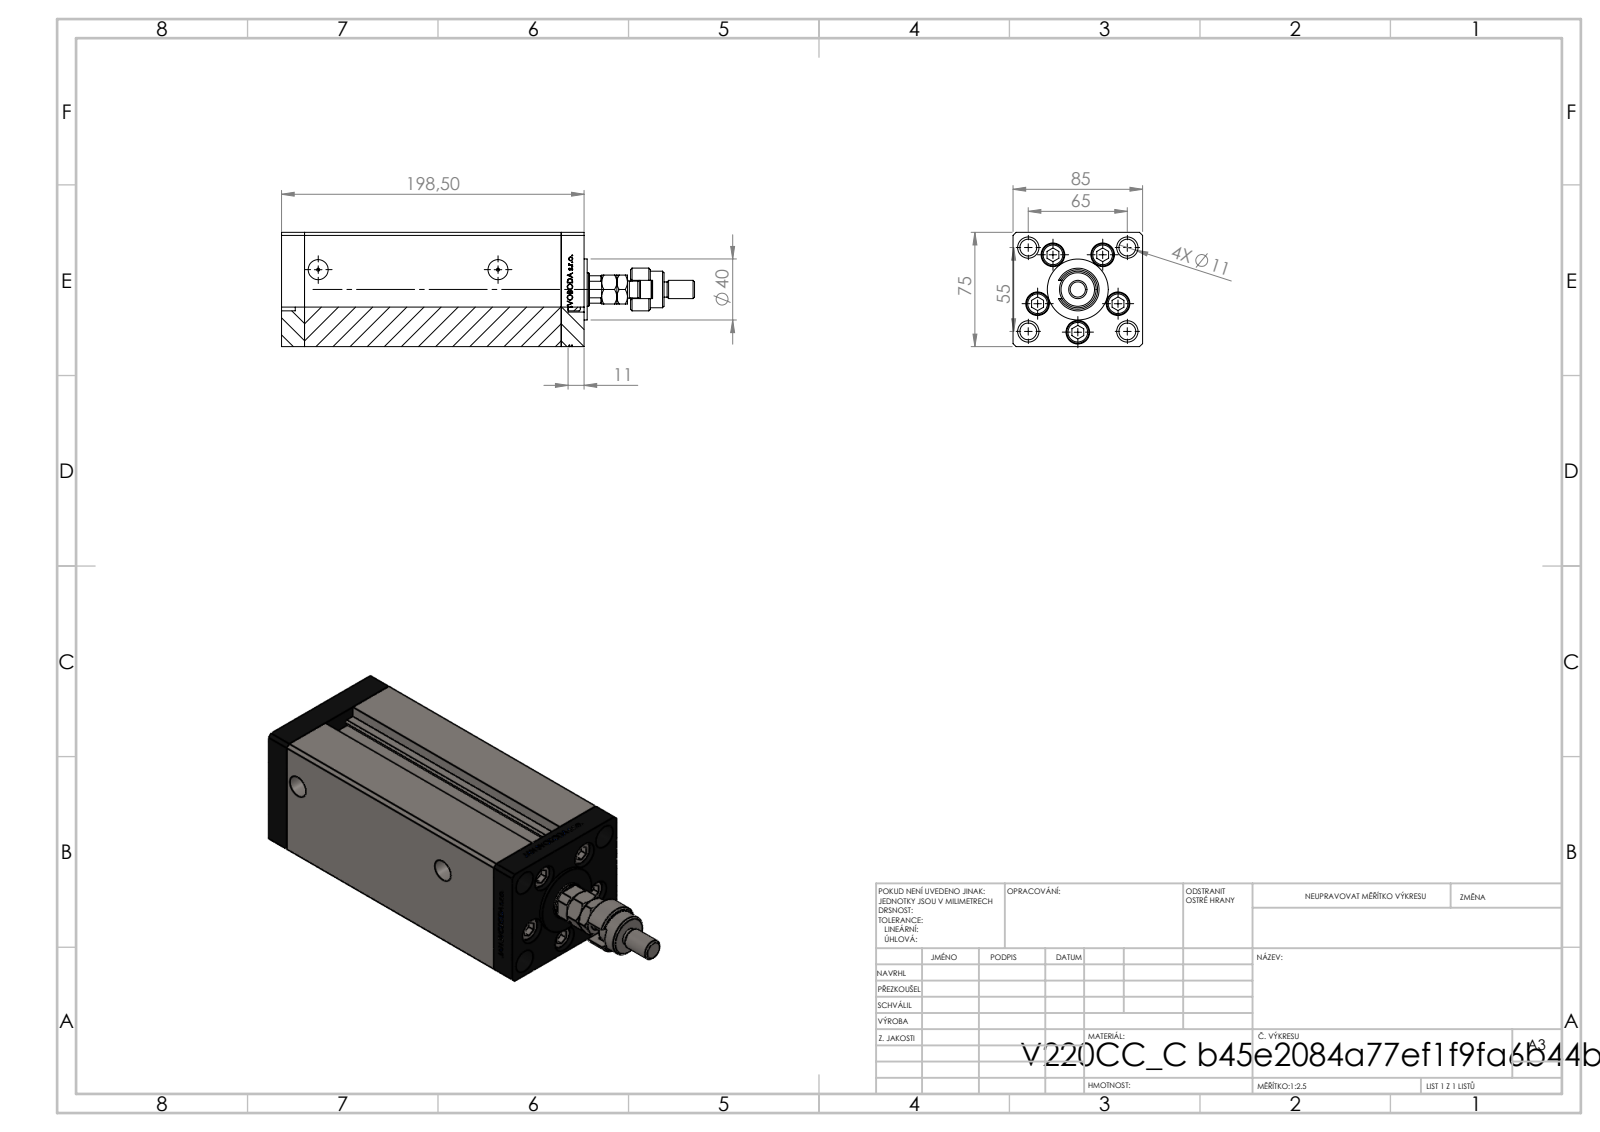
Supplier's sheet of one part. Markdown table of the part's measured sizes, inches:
| quantity | value |
| --- | --- |
| part name | V220C BACK_C; ALLEN BOLT; MFA; FEMALE_PART_FOR_DFA (+3 more) |
| STEP written by | SolidWorks 2019 (CONFIG_CONTROL_DESIGN) |
| units | inches |
| bodies | 15 solids, 1260 faces (574 planar, 180 cylindrical, 506 other) |
| overall size | 10.669 × 3.346 × 2.953 |
| volume | 64.87 in³ |
| surface area | 311.9 in² |
| round holes (diameter × count) | 0.433 × 9, 0.61 × 5, 0.394 × 4, 0.551 × 4, 0.079 × 2, 0.518 × 2, 0.531 × 1, 0.571 × 1, 0.866 × 1 |
| round bosses / shafts (diameter × count) | 0.315 × 5, 0.571 × 4, 1.575 × 1, 1.102 × 1, 0.945 × 1, 0.709 × 1, 0.472 × 1, 0.433 × 1 |
| partial cylindrical surfaces (radius × count) | 0.037 × 2, 0.384 × 1, 0.413 × 1 |
| main face-to-face distances | 3.346, 2.953, 6.634, 0.591, 7.224, 0.413, 7.815, 1.348, 2.539, 2.697 |
| hole center spacings | 1.102, 1.676, 0.664, 0.755, 1.273, 1.28, 1.324, 1.47 |
